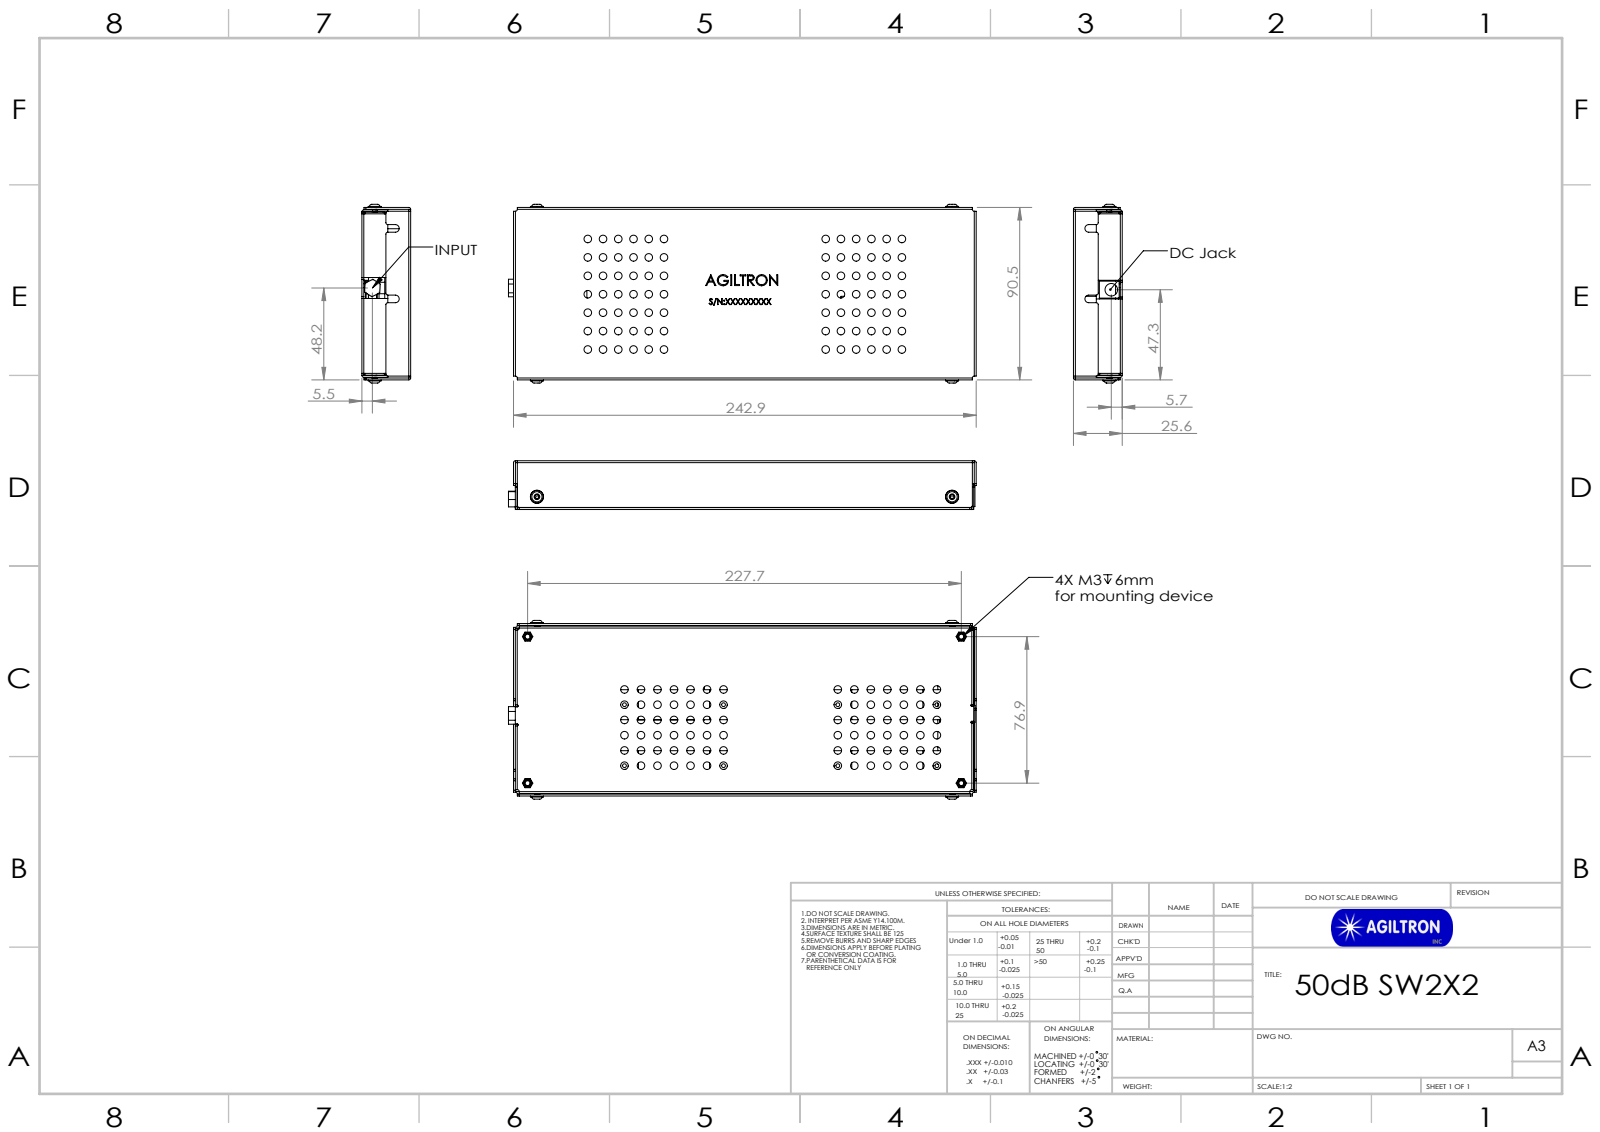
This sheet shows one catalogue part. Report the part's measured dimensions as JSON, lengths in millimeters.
{"part_name": "4 EO PCB; 1001870_4 EO BOTTOM COVER ASM; 97654A674_18-8 Stainless Steel Flanged Button Head Screw_97654A674; 4 EO COVER TOP (+8 more)", "step_written_by": "SolidWorks 2017 (CONFIG_CONTROL_DESIGN)", "units": "millimeters", "bodies": {"solids": 27, "faces": 882, "planar": 452, "cylindrical": 358, "other": 72}, "overall_size": [245.55, 93.8, 25.6], "volume_mm3": 136009, "surface_area_mm2": 190350, "round_holes": [[4, 168], [4.2, 14], [2, 8], [2.55, 6], [3.5, 4], [6.6, 1]], "round_bosses_or_shafts": [[6.3, 8], [4.19, 6], [3.59, 6], [3, 2], [6, 1]], "partial_cylinders_radius": [[1, 34], [2, 22], [0.2, 8], [0.5, 8], [1.2, 8]], "face_to_face_distances": [1, 24.6, 12, 11, 12.6, 13.6, 23.6, 25.6, 1.6, 89.5], "hole_center_spacings": [11.8, 19.1, 8, 8.67, 27.21, 17.34, 18.2, 16]}
